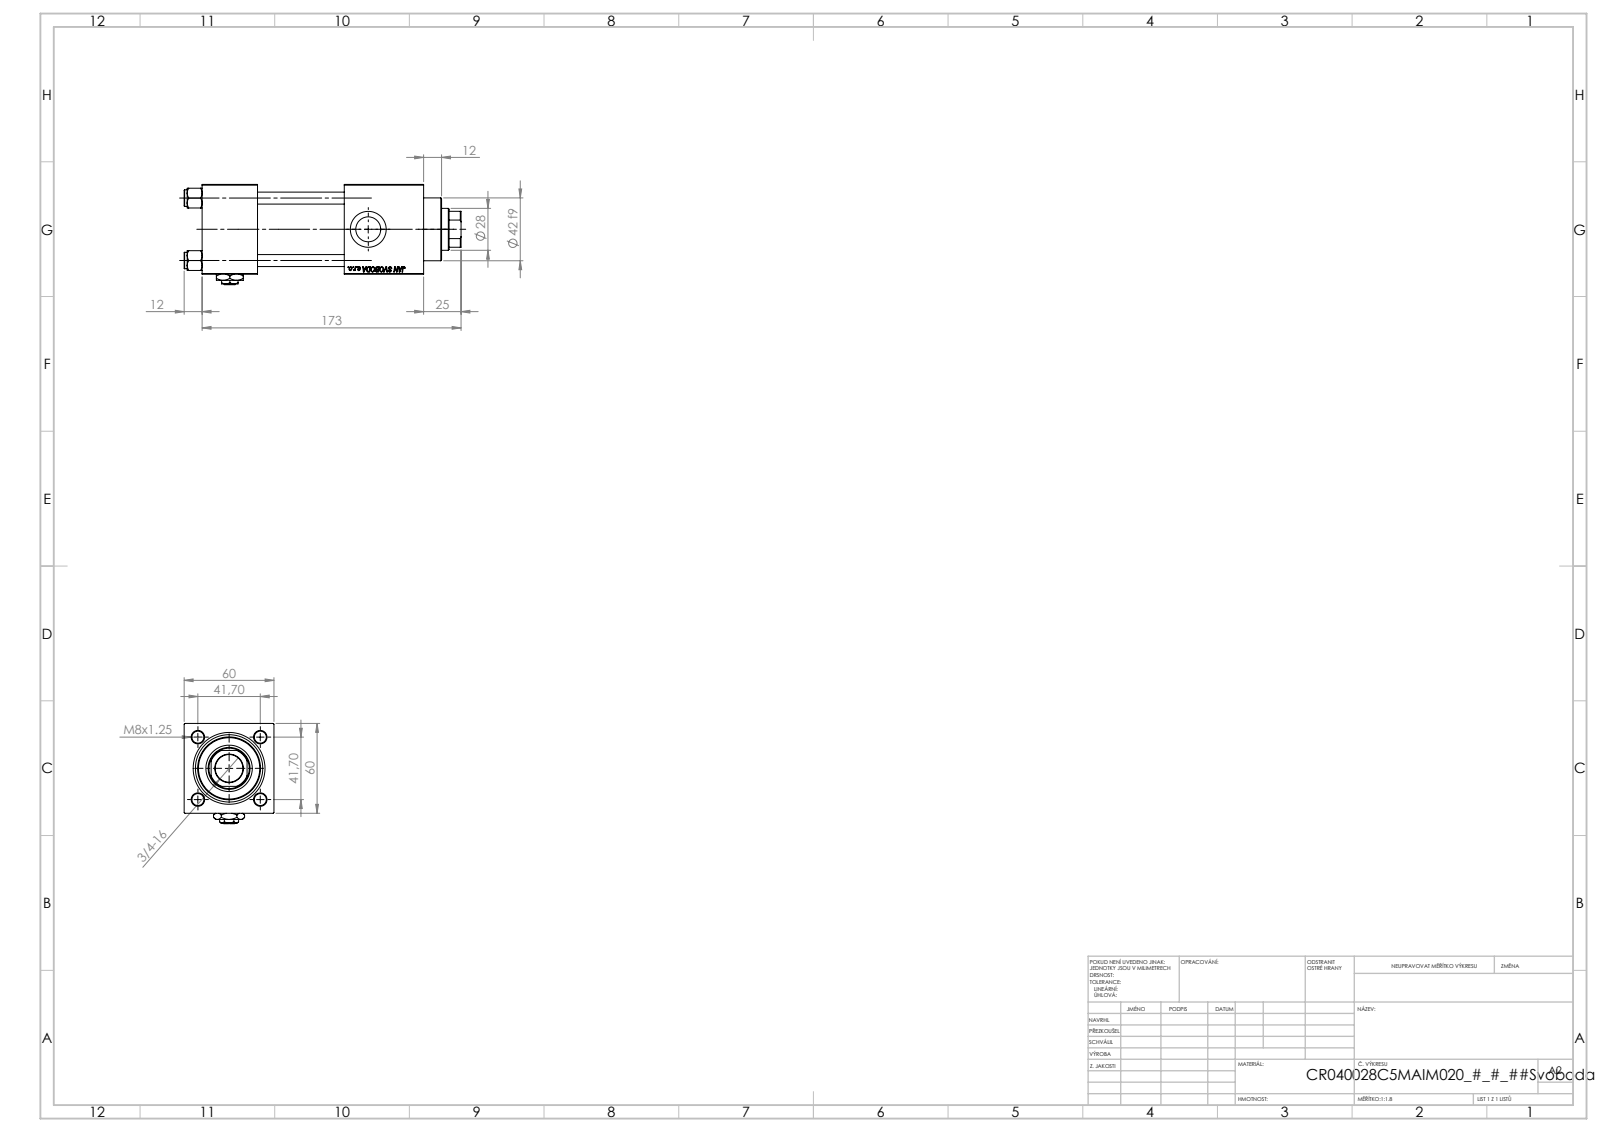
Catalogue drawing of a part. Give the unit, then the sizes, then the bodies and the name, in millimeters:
Units: millimetres
Overall size (bounding box): 185 × 67 × 60
Round holes (diameter × count): ⌀8 ×4, ⌀7 ×2, ⌀16.66 ×2, ⌀24 ×2, ⌀18.5 ×1, ⌀28 ×1, ⌀31 ×1, ⌀40 ×1, ⌀45 ×1
Round bosses / shafts (diameter × count): ⌀11 ×4, ⌀46 ×1, ⌀42 ×1
Partial cylindrical surfaces — rounded edges, fillets, slot ends (radius × count): R13.5 ×1
Main face-to-face distances: 60, 37, 58, 95, 53, 119.3, 82.3, 24.3, 148, 111
Hole centre spacings: 29.49, 41.7, 58.97
Volume: 422 346 mm³ · Surface area: 113 171 mm²
Bodies: 12 solids, 1202 faces (550 planar, 94 cylindrical, 558 other)
Part name (STEP PRODUCT): V215CR_VCP_C; V215CR_C_Body; V215CR_C_TYCINKA; Zatka_pro_OIL_PORT (+2 more)
STEP written by: SolidWorks 2019 (CONFIG_CONTROL_DESIGN)
